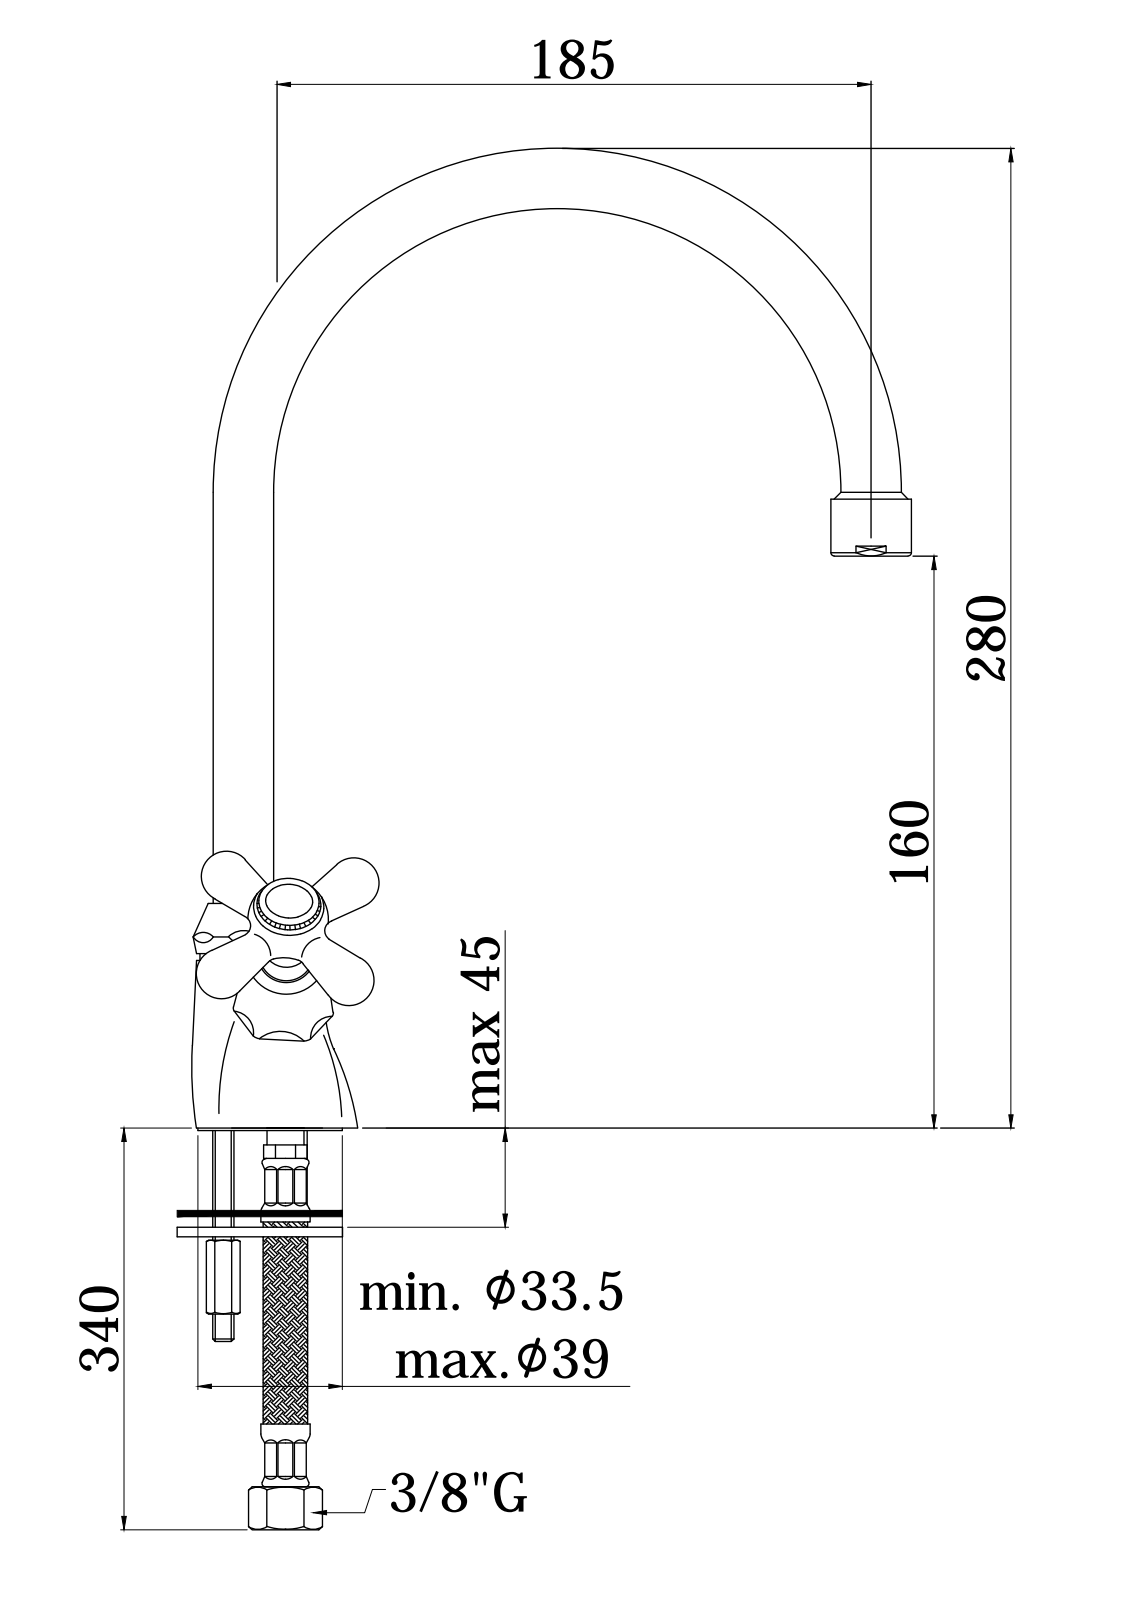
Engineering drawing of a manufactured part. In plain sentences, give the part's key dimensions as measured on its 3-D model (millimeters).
The part is named "IRV180CR". Its 3-D file was written by "CREO PARAMETRIC BY PTC INC, 2020044 (CONFIG_CONTROL_DESIGN)". It is 1 solid with 450 faces: 136 planar, 102 cylindrical and 212 other. Overall it measures 278.1 by 223.65 by 183.98 millimeters. Its volume is 226 252 cubic millimeters and its surface area 65 567 square millimeters. Round holes: 4 of diameter 9, 2 of diameter 8, 2 of diameter 11, 2 of diameter 15.7, 2 of diameter 18, 2 of diameter 19, 2 of diameter 21, 2 of diameter 21.5, 2 of diameter 23, 1 of diameter 6, 1 of diameter 6.8, 1 of diameter 16. Round bosses or shafts: 4 of diameter 18, 2 of diameter 26.3, 2 of diameter 13.5, 1 of diameter 34, 1 of diameter 26.4, 1 of diameter 23.6, 1 of diameter 18.8. Partial cylindrical surfaces (rounded edges, fillets, slot ends): 2 of radius 14.5, 1 of radius 15. The main face-to-face distances are 26.49, 22, 24.01, 152.4, 1.3, 151.1, 46.01, 28.5, 2, 40.1. The hole center spacings are 7, 13.38, 13.89, 0.6, 11.4, 12, 14.
